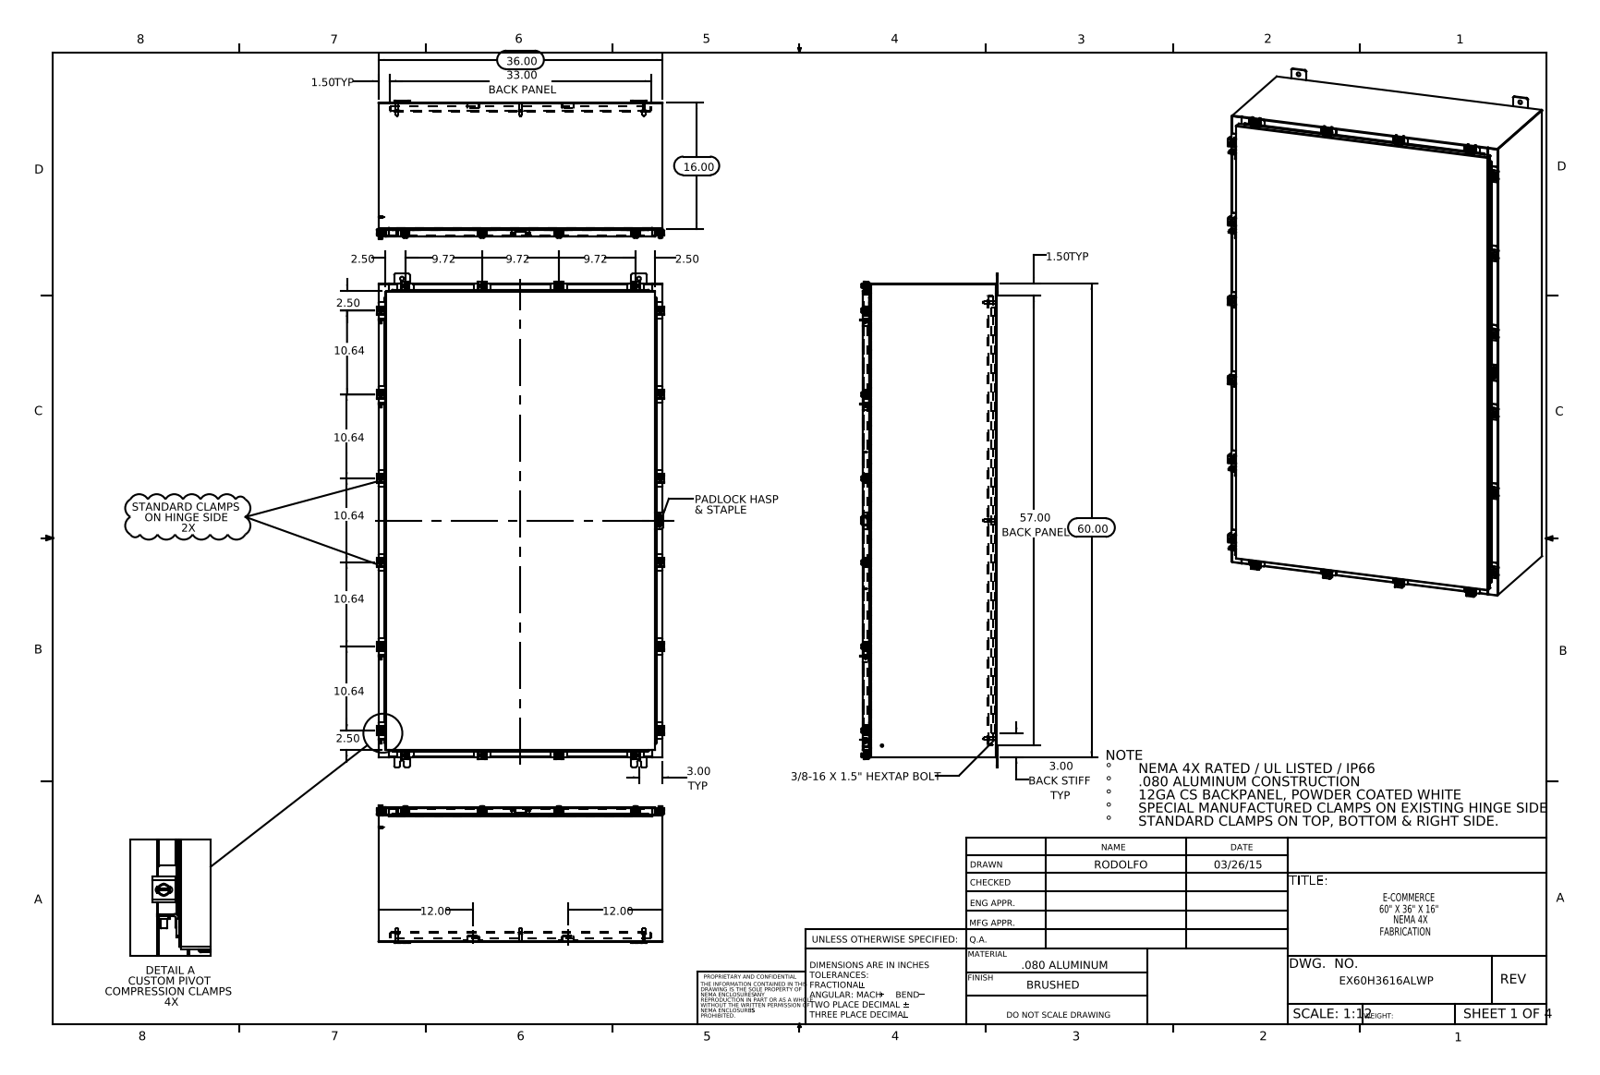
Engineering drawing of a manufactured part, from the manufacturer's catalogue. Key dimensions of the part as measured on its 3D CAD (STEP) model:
Part name (STEP PRODUCT): 10_30 CD Stud; EX60H3616ALWP Padlock Staple; N-WMT04X30402202210-00 Clamp Top; N-WMT04X30402202210-00 22104005_DEFAULT (+8 more)
STEP written by: SolidWorks 2014 (CONFIG_CONTROL_DESIGN)
Units: inches
Bodies: 140 solids, 3424 faces (1773 planar, 1319 cylindrical, 332 other)
Overall size (bounding box): 62.5 × 36.421 × 17.453
Volume: 850 in³ · Surface area: 21 217 in²
Round holes (diameter × count): ⌀0.213 ×20, ⌀0.26 ×20, ⌀0.5 ×12, ⌀0.25 ×9, ⌀0.125 ×1
Round bosses / shafts (diameter × count): ⌀0.5 ×20, ⌀0.25 ×20, ⌀0.399 ×16, ⌀0.625 ×8, ⌀0.375 ×8, ⌀0.33 ×8, ⌀0.157 ×8, ⌀0.14 ×8
Partial cylindrical surfaces — rounded edges, fillets, slot ends (radius × count): R0.06 ×84, R0.141 ×40, R0.013 ×38, R0.12 ×36, R0.088 ×34, R0.09 ×32, R0.05 ×29, R0.145 ×28
Main face-to-face distances: 0.075, 16.9, 16.826, 0.104, 16.975, 35.925, 1, 1.075, 15.826, 15.9
Hole centre spacings: 1.969, 2.224, 2.347, 13.972, 14.729, 16.126, 27.625, 29.744
